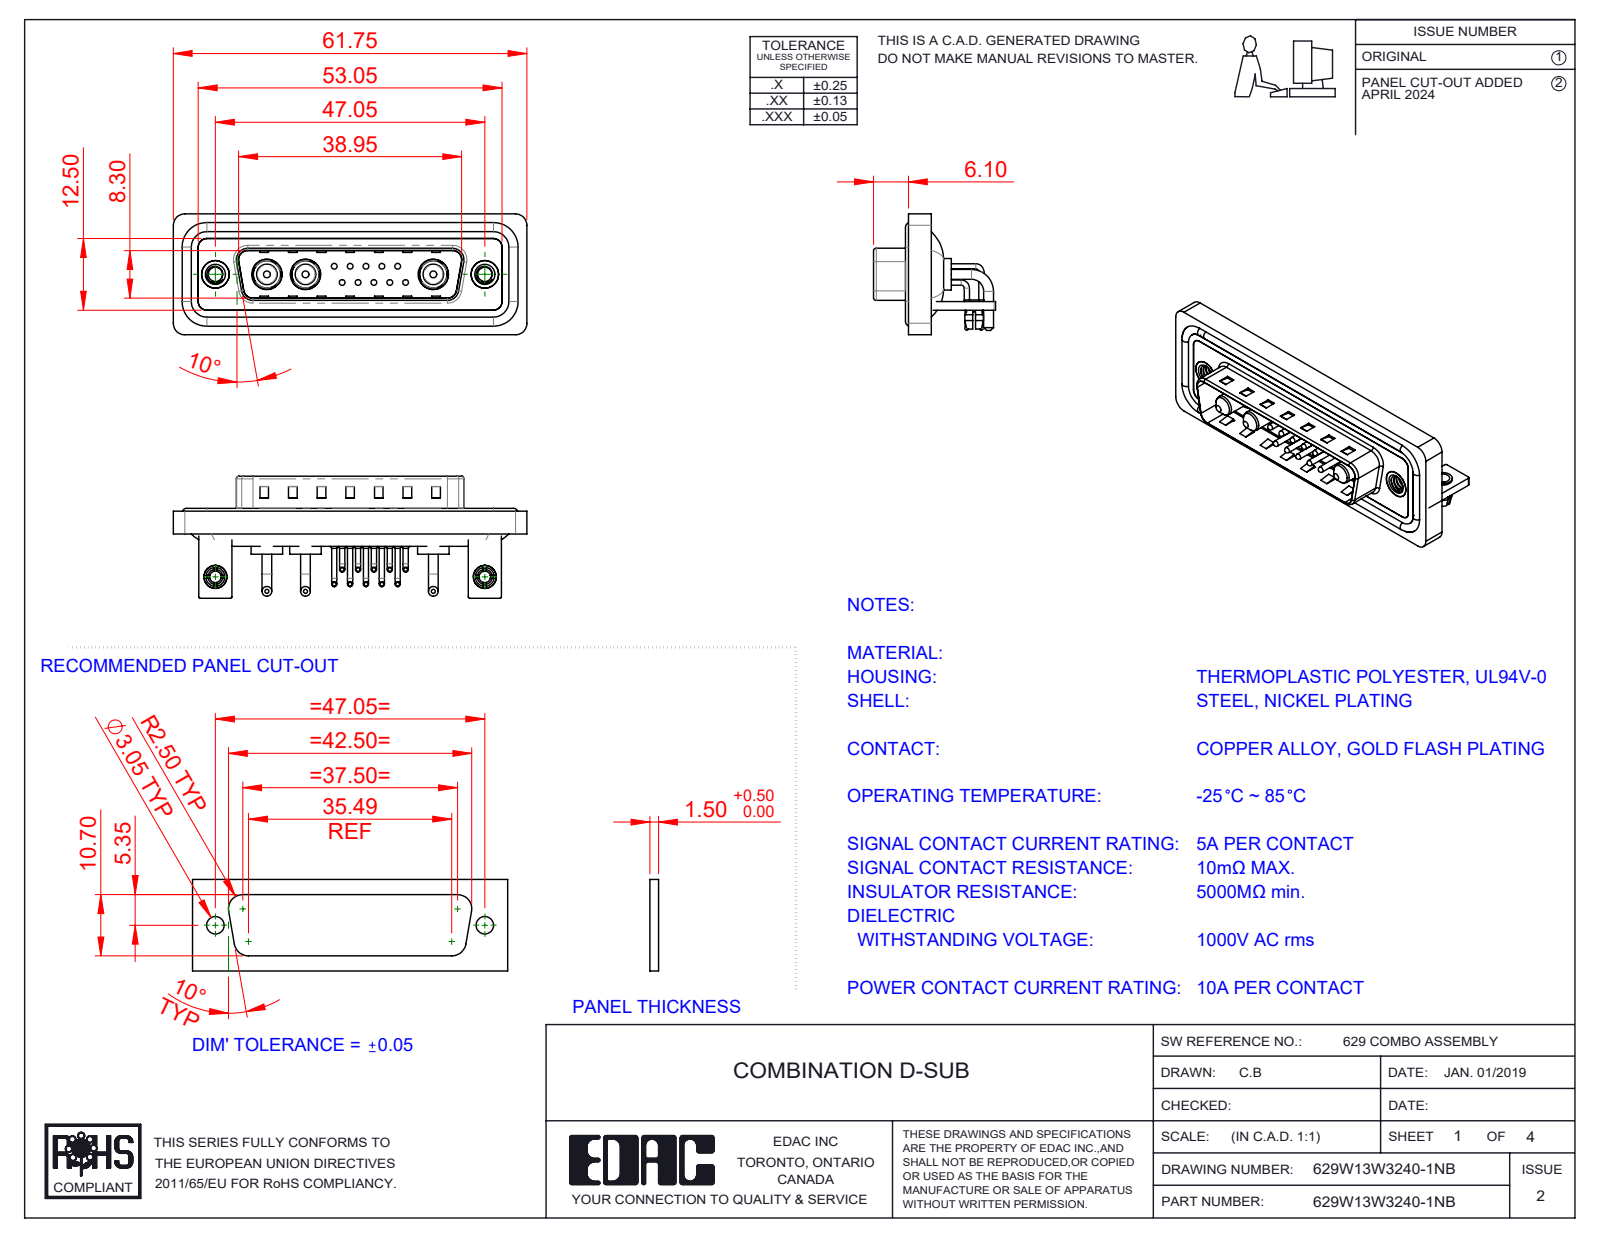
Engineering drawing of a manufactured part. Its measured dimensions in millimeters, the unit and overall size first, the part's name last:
Units: millimetres
Overall size (bounding box): 61.75 × 21.3 × 21.1
Round holes (diameter × count): ⌀2 ×12, ⌀0.75 ×10, ⌀1.6 ×10, ⌀2.5 ×4, ⌀4.85 ×3, ⌀5.3 ×3, ⌀3.2 ×2, ⌀4 ×2, ⌀4.8 ×2, ⌀5 ×2
Round bosses / shafts (diameter × count): ⌀0.9 ×20, ⌀1.5 ×10, ⌀1 ×10, ⌀0.65 ×10, ⌀1.7 ×6, ⌀1.6 ×4, ⌀5.5 ×3, ⌀5.2 ×3
Partial cylindrical surfaces — rounded edges, fillets, slot ends (radius × count): R2 ×19, R1.5 ×18, R0.25 ×16, R1.01 ×10, R0.5 ×9, R1.6 ×8, R0.6 ×4, R0.65 ×4
Main face-to-face distances: 0.4, 1.5, 0.8, 2.9, 2.1, 1.1, 4.1, 1.6, 3.7, 4.5
Hole centre spacings: 3.16, 2.77, 5.04, 5.54, 7.49, 5.03, 8.31, 10.11
Volume: 7 744 mm³ · Surface area: 13 142 mm²
Bodies: 27 solids, 1842 faces (947 planar, 661 cylindrical, 234 other)
Part name (STEP PRODUCT): 629Combo Contact Row 1; 629Combo Contact Row 2; Power Pin_10A RA; 629W13W3140-1NB (+7 more)
STEP written by: SolidWorks 2023 (CONFIG_CONTROL_DESIGN)
